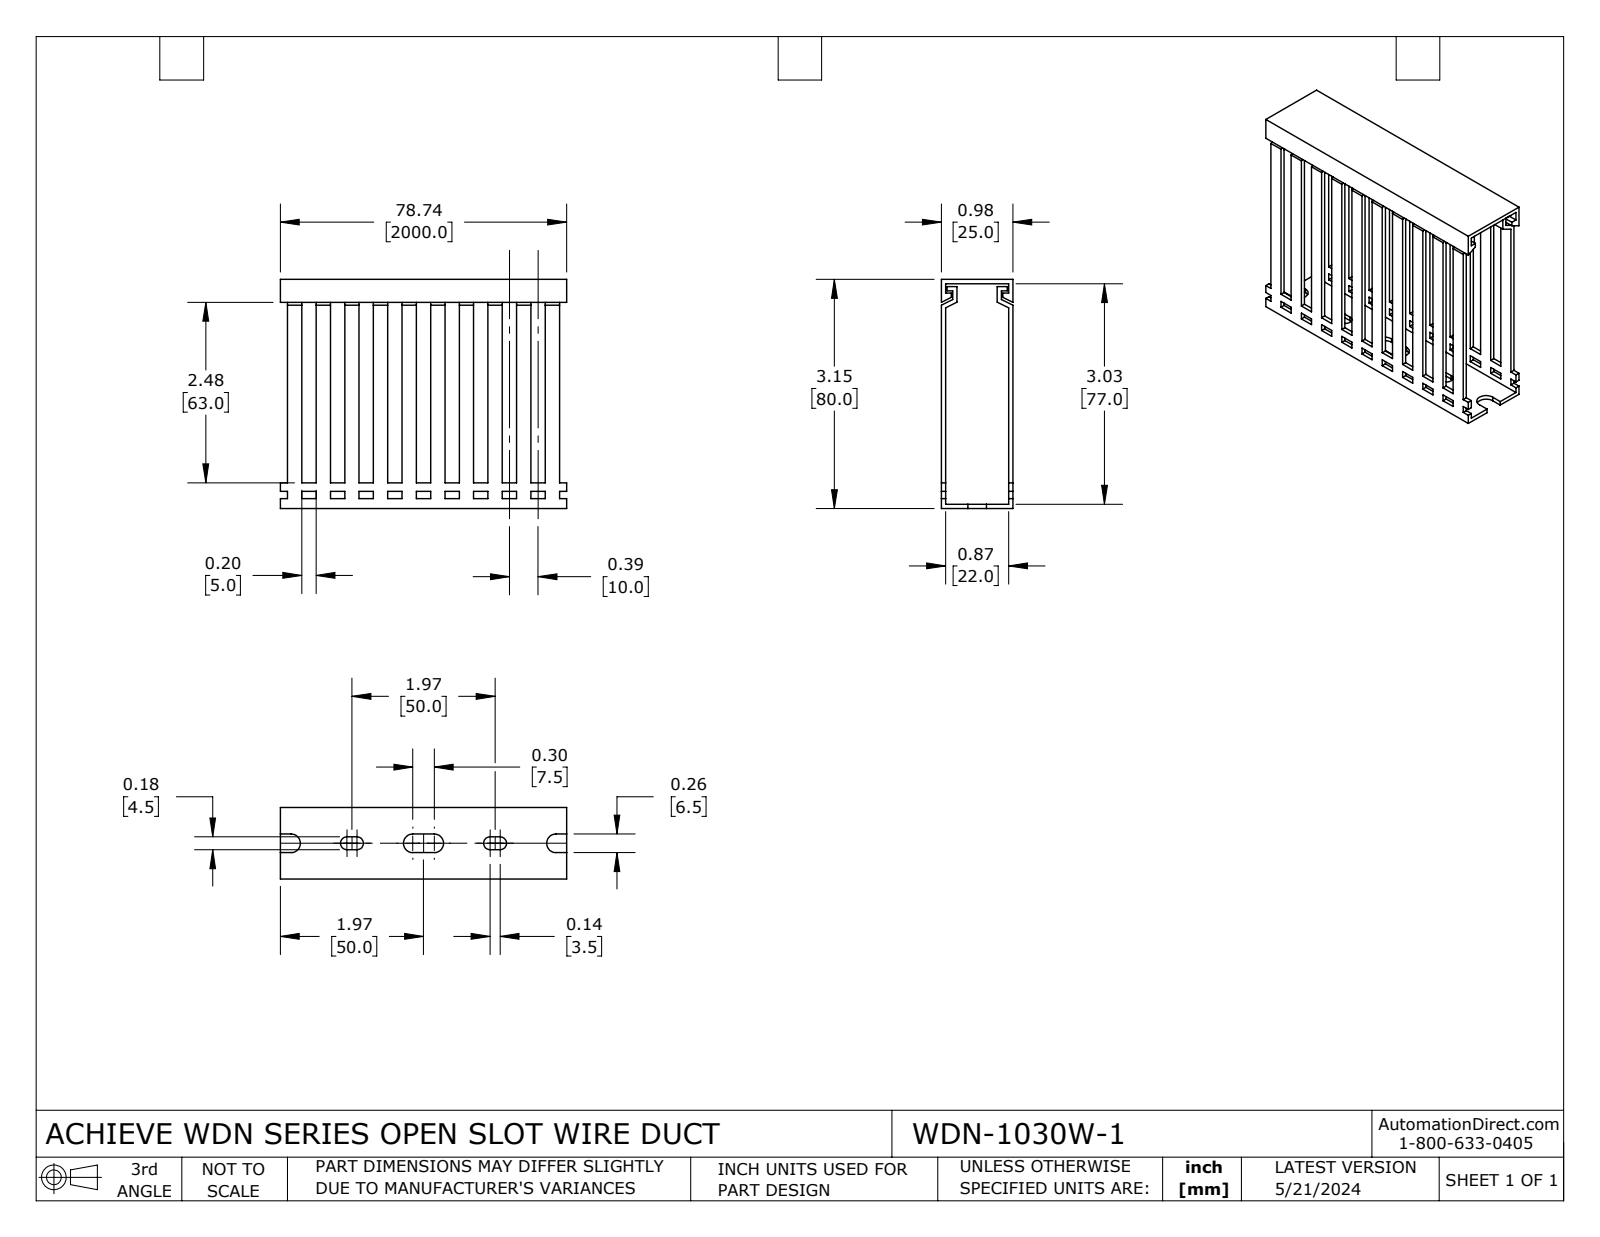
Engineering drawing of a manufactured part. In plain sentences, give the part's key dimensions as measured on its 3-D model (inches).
The part is named "WDN-1030W-1". Its 3-D file was written by "SolidWorks 2023 (CONFIG_CONTROL_DESIGN)". It is 2 solids with 336 faces: 324 planar, 12 cylindrical and 0 other. Overall it measures 3.937 by 3.15 by 0.984 inches. Its volume is 1.38 cubic inches and its surface area 55.16 square inches. Partial cylindrical surfaces (rounded edges, fillets, slot ends): 4 of radius 0.089, 4 of radius 0.128. The main face-to-face distances are 0.059, 0.984, 0.925, 0.197, 3.091, 0.394, 0.866, 0.787, 0.591, 3.15.
